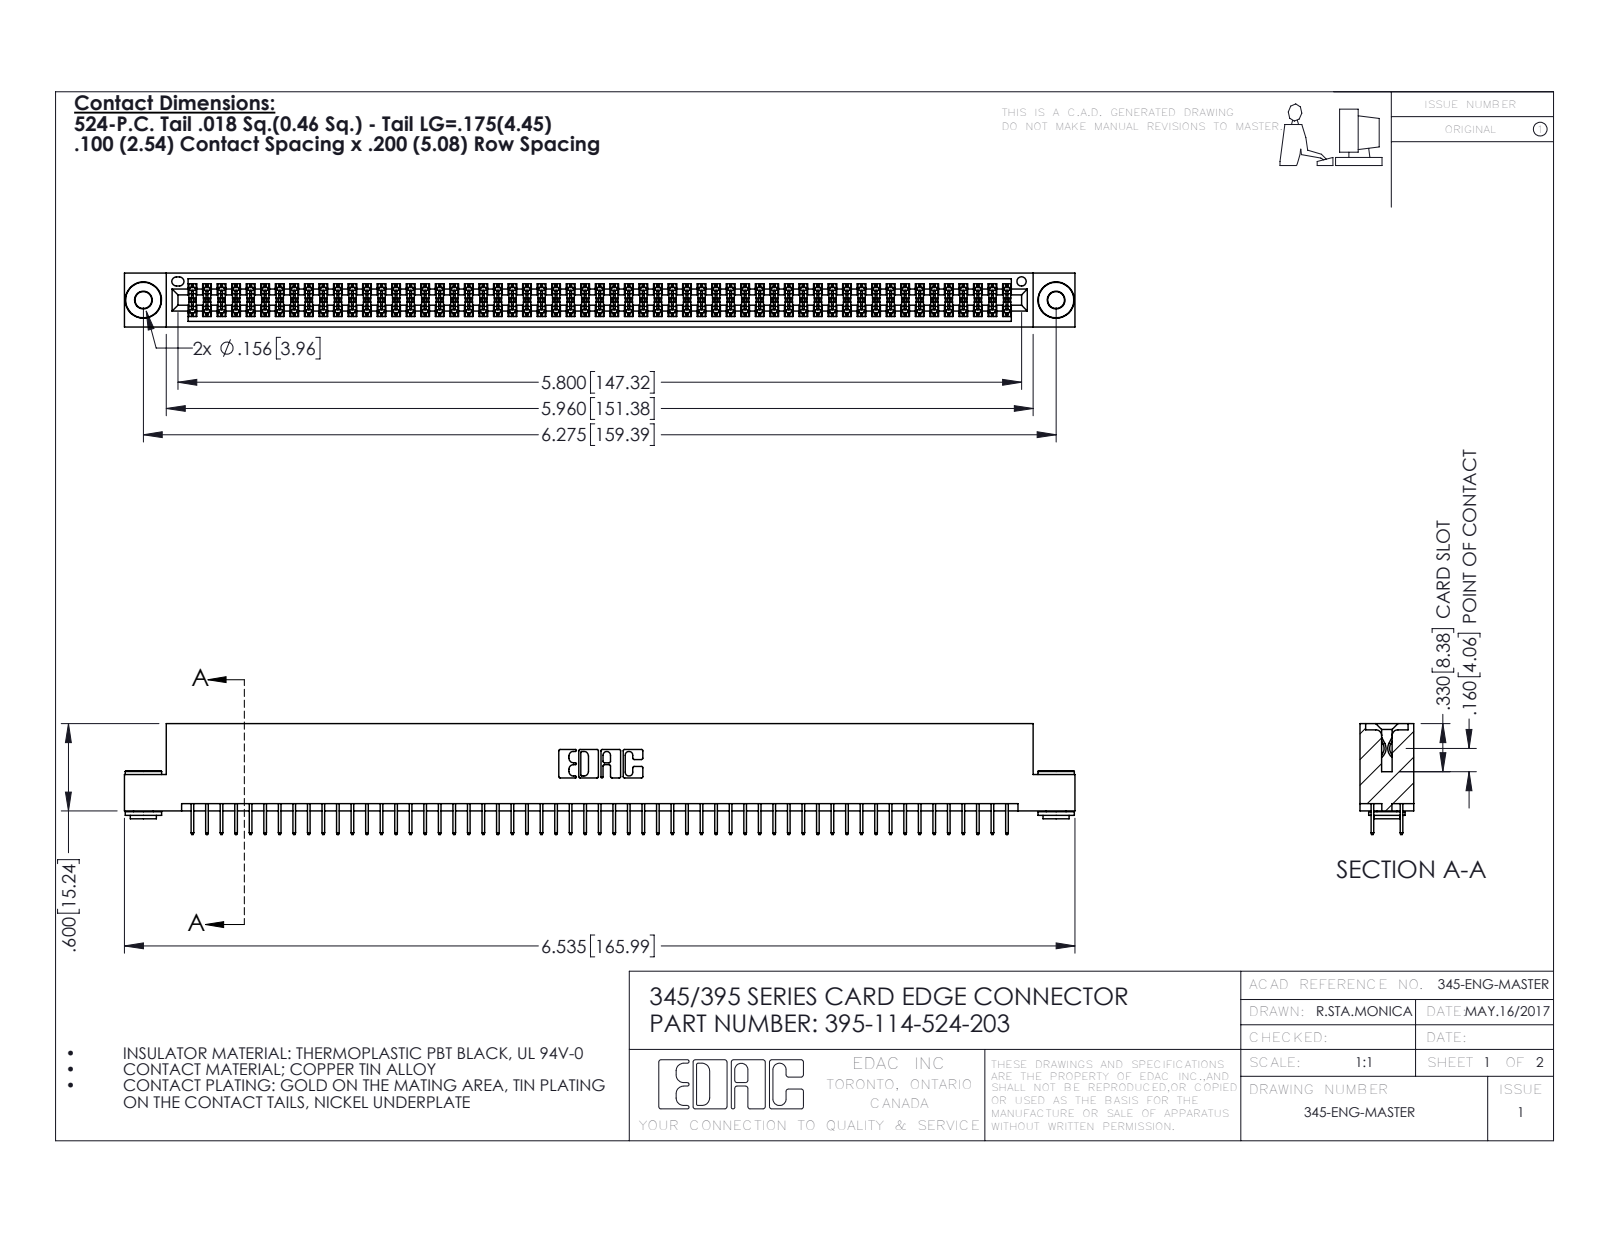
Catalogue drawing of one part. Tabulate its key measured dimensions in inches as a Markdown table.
| quantity | value |
| --- | --- |
| part name | 395-114-524-203; 345-250-002_345-250-002-102; 345 Part_Flush Mounting Lugs - 0.156 Dia-TH; 345-292-001_345-293-124 |
| STEP written by | SolidWorks 2016 (CONFIG_CONTROL_DESIGN) |
| units | inches |
| bodies | 117 solids, 6320 faces (4536 planar, 1776 cylindrical, 8 other) |
| overall size | 6.535 × 0.762 × 0.37 |
| volume | 0.983 in³ |
| surface area | 36.97 in² |
| round holes (diameter × count) | 0.116 × 2, 0.156 × 2, 0.064 × 1 |
| round bosses / shafts (diameter × count) | 0.25 × 2, 0.18 × 2, 0.136 × 2 |
| partial cylindrical surfaces (radius × count) | 0.006 × 171, 0.01 × 22, 0.007 × 6, 0.031 × 6, 0.026 × 3, 0.014 × 2, 0.019 × 2, 0.022 × 2 |
| main face-to-face distances | 0.072, 0.298, 0.2, 0.37, 0.025, 0.098, 0.272, 0.225, 0.072, 0.175 |
| hole center spacings | 0.27, 6.039, 6.275 |
